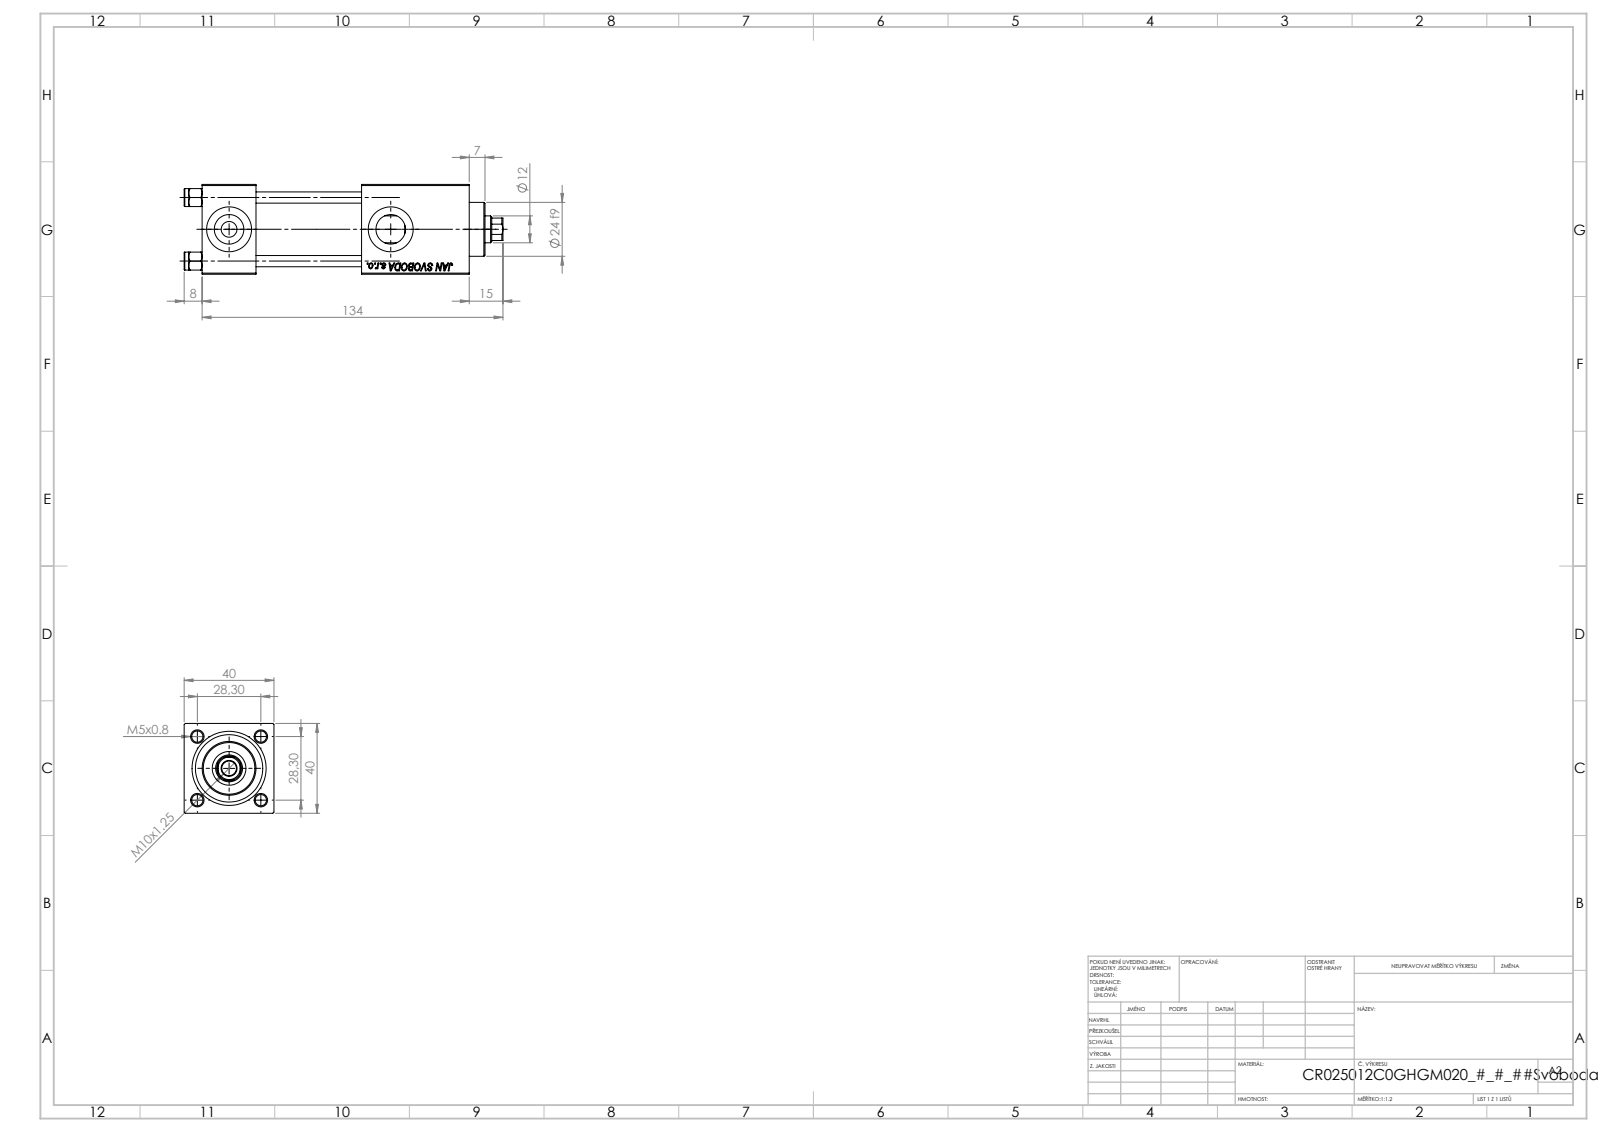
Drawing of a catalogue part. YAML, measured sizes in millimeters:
part_name: "V215CR_C_TYCINKA; NUT_M5_C; V215CR_C_Body; V215CR_VCP_C (+1 more)"
step_written_by: "SolidWorks 2019 (CONFIG_CONTROL_DESIGN)"
units: millimeters
bodies: {solids: 11, faces: 1147, planar: 525, cylindrical: 86, other: 536}
overall_size: [142, 40, 40]
volume: 142389
surface_area: 54442
round_holes:
  - {diameter: 5, count: 4}
  - {diameter: 20, count: 3}
  - {diameter: 7, count: 2}
  - {diameter: 13.16, count: 2}
  - {diameter: 6.5, count: 1}
  - {diameter: 12, count: 1}
  - {diameter: 15, count: 1}
  - {diameter: 25, count: 1}
  - {diameter: 30, count: 1}
round_bosses_or_shafts:
  - {diameter: 8, count: 4}
  - {diameter: 31, count: 1}
  - {diameter: 24, count: 1}
partial_cylinders:
  - {radius: 5.5, count: 1}
face_to_face_distances: [40, 24, 90.3, 66.3, 48, 71, 47, 19.3, 119, 95]
hole_center_spacings: [20.01, 28.3, 40.02, 72]
